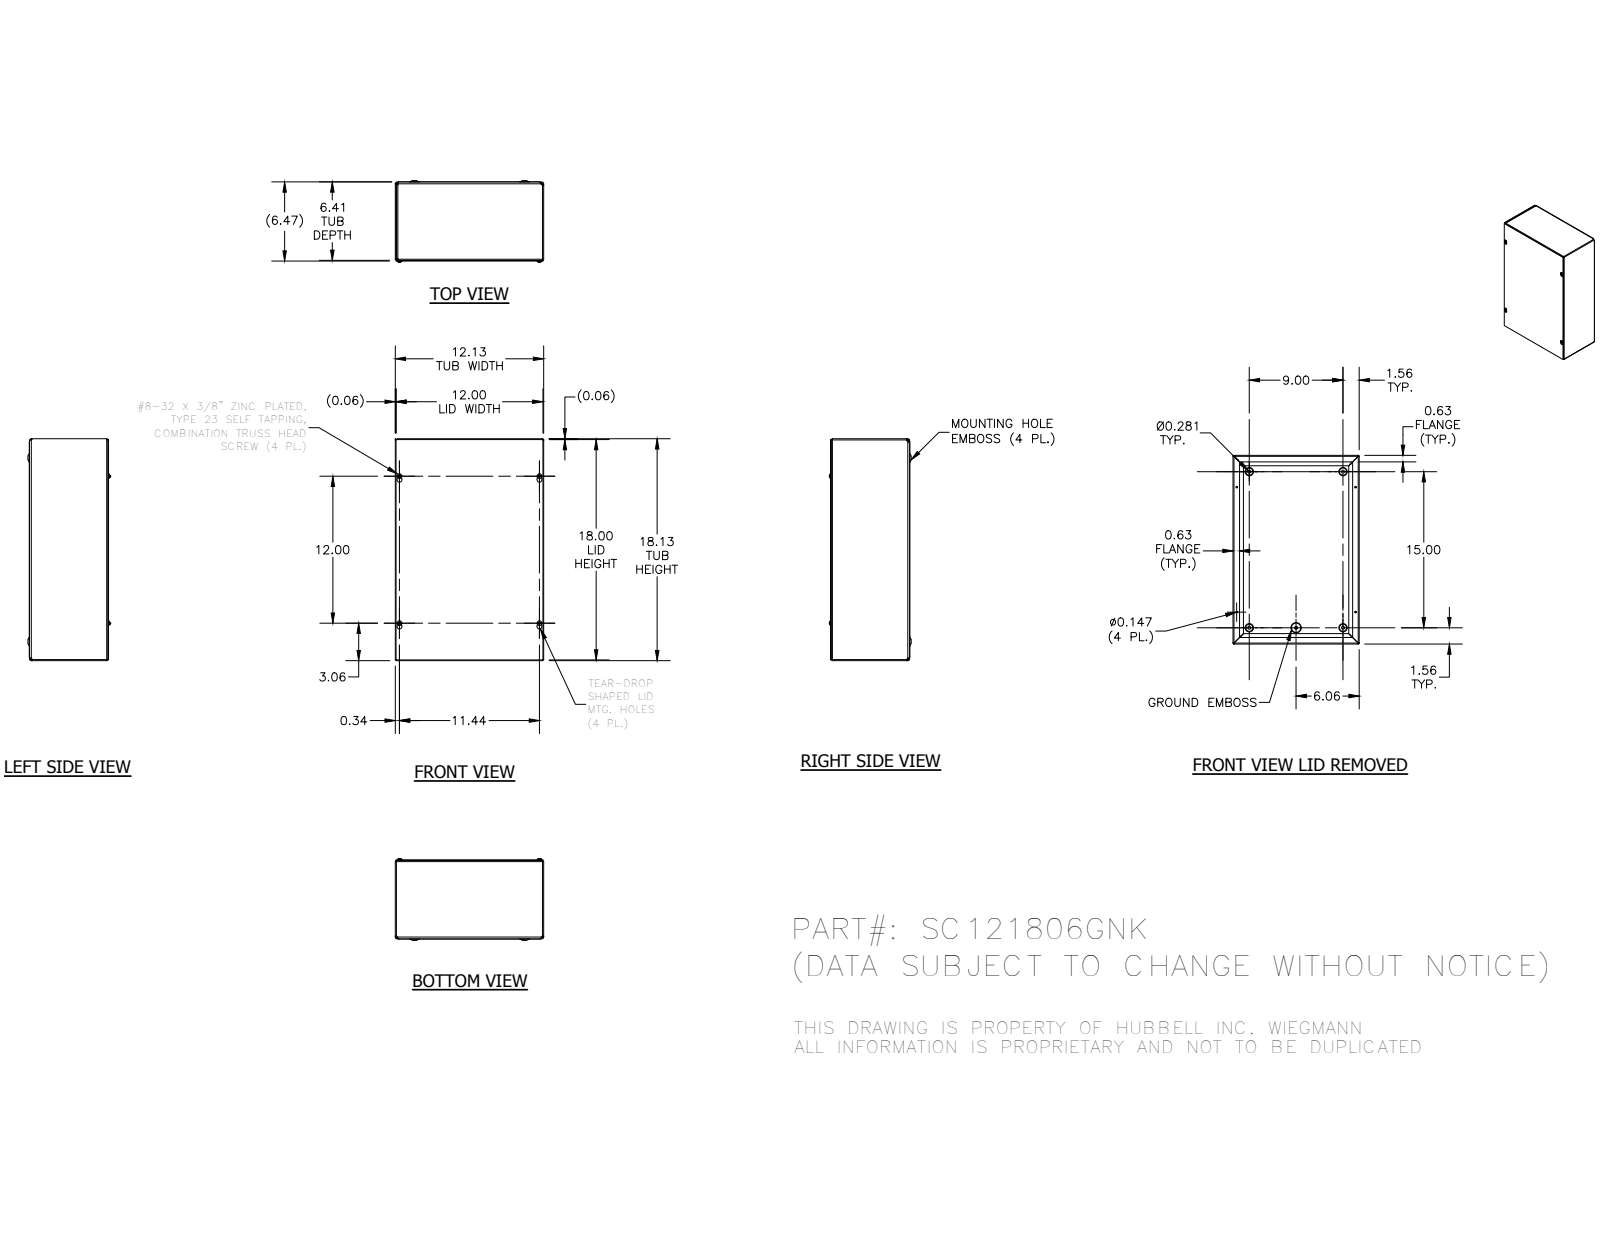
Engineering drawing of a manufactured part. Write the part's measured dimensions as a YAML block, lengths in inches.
part_name: "SC1218GNKBKP; SC121806GNKWRA; SC1218GNKLID; 34056 (+1 more)"
step_written_by: "Autodesk Inventor 2014 (AUTOMOTIVE_DESIGN)"
units: inches
bodies: {solids: 7, faces: 358, planar: 133, cylindrical: 73, other: 152}
overall_size: [18.125, 12.125, 6.693]
volume: 55.33
surface_area: 1800
round_holes:
  - {diameter: 0.147, count: 4}
  - {diameter: 0.3, count: 4}
  - {diameter: 0.165, count: 1}
round_bosses_or_shafts:
  - {diameter: 0.384, count: 4}
  - {diameter: 0.164, count: 4}
  - {diameter: 0.228, count: 1}
partial_cylinders:
  - {radius: 0.031, count: 8}
  - {radius: 0.093, count: 8}
  - {radius: 0.055, count: 4}
  - {radius: 0.062, count: 4}
  - {radius: 0.094, count: 4}
  - {radius: 0.117, count: 4}
  - {radius: 0.124, count: 4}
  - {radius: 0.125, count: 4}
face_to_face_distances: [0.062, 6.343, 6.405, 0.063, 6.406, 6.468, 18.063, 0.062, 12.125, 12.063]
hole_center_spacings: [4.5, 9, 10.328, 10.328, 11.437, 12, 13.554, 13.556]
